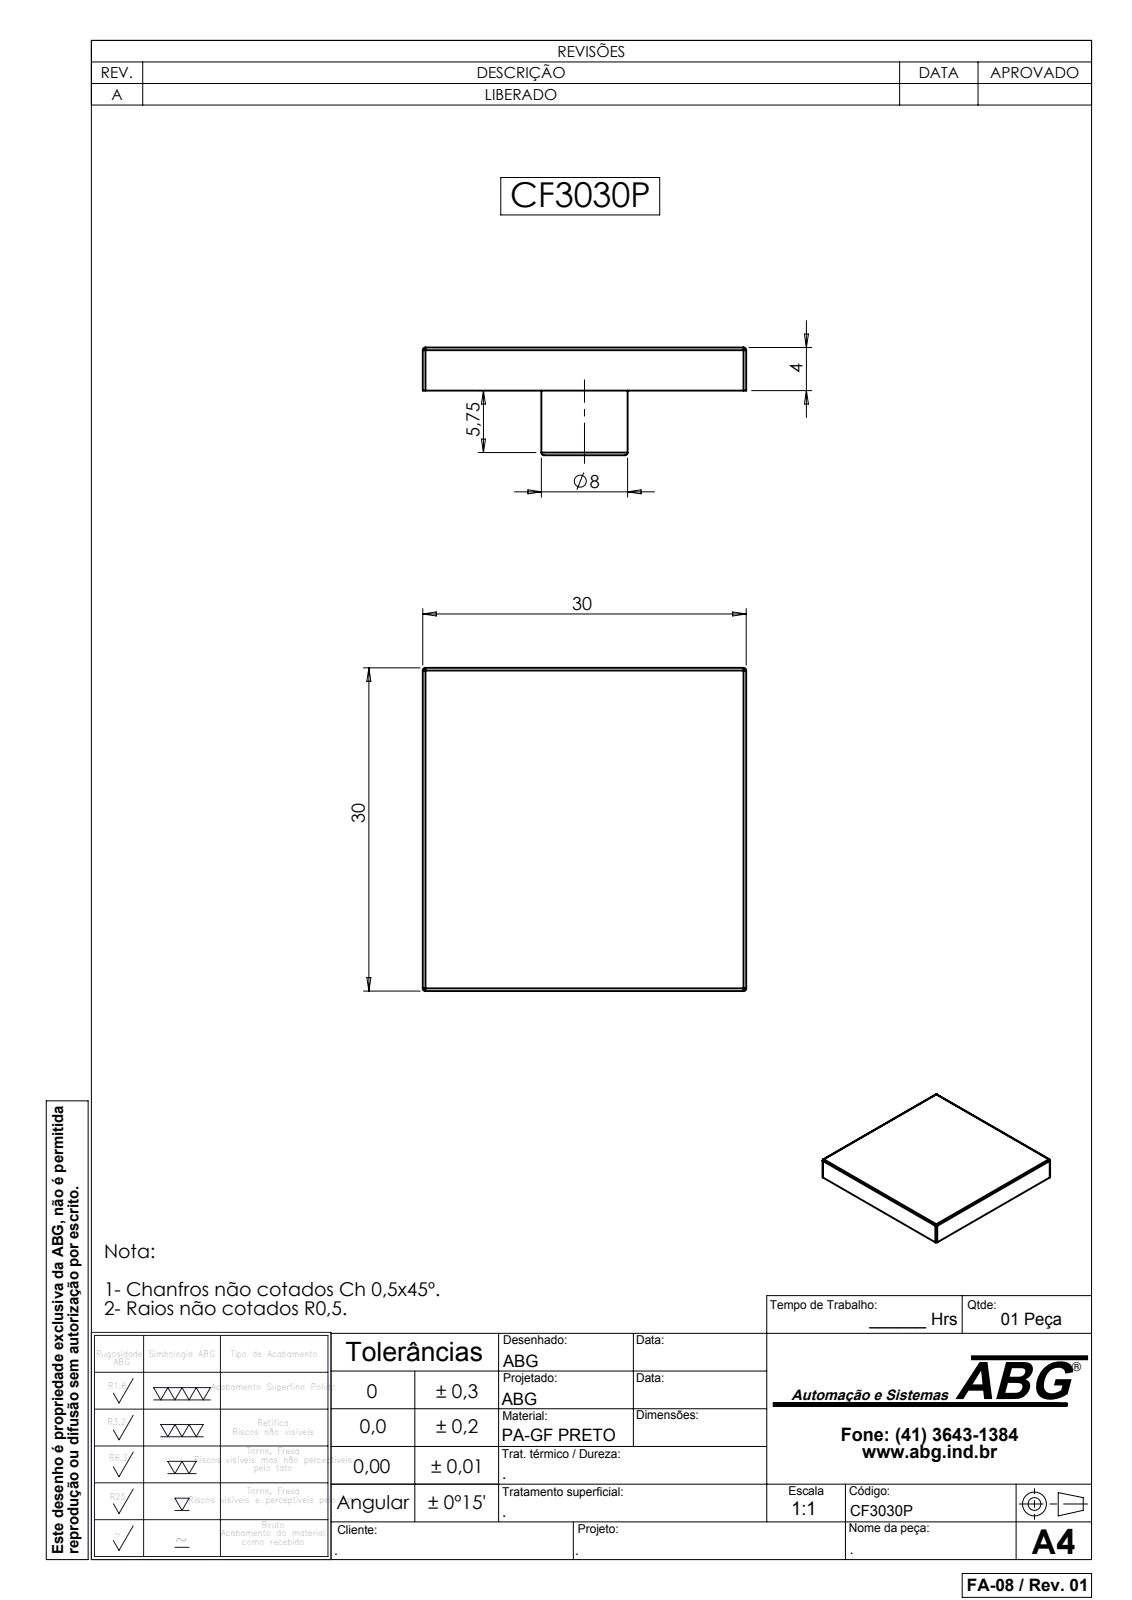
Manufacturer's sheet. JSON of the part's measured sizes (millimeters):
{"part_name": "CF3030P", "step_written_by": "SolidWorks 2007 (CONFIG_CONTROL_DESIGN)", "units": "millimeters", "bodies": {"solids": 1, "faces": 28, "planar": 8, "cylindrical": 12, "other": 8}, "overall_size": [30, 30, 10], "volume_mm3": 3730, "surface_area_mm2": 2524, "round_holes": [[6, 1]], "round_bosses_or_shafts": [[8, 1]], "partial_cylinders_radius": [[0.25, 8]], "face_to_face_distances": [4, 30, 10, 6]}
